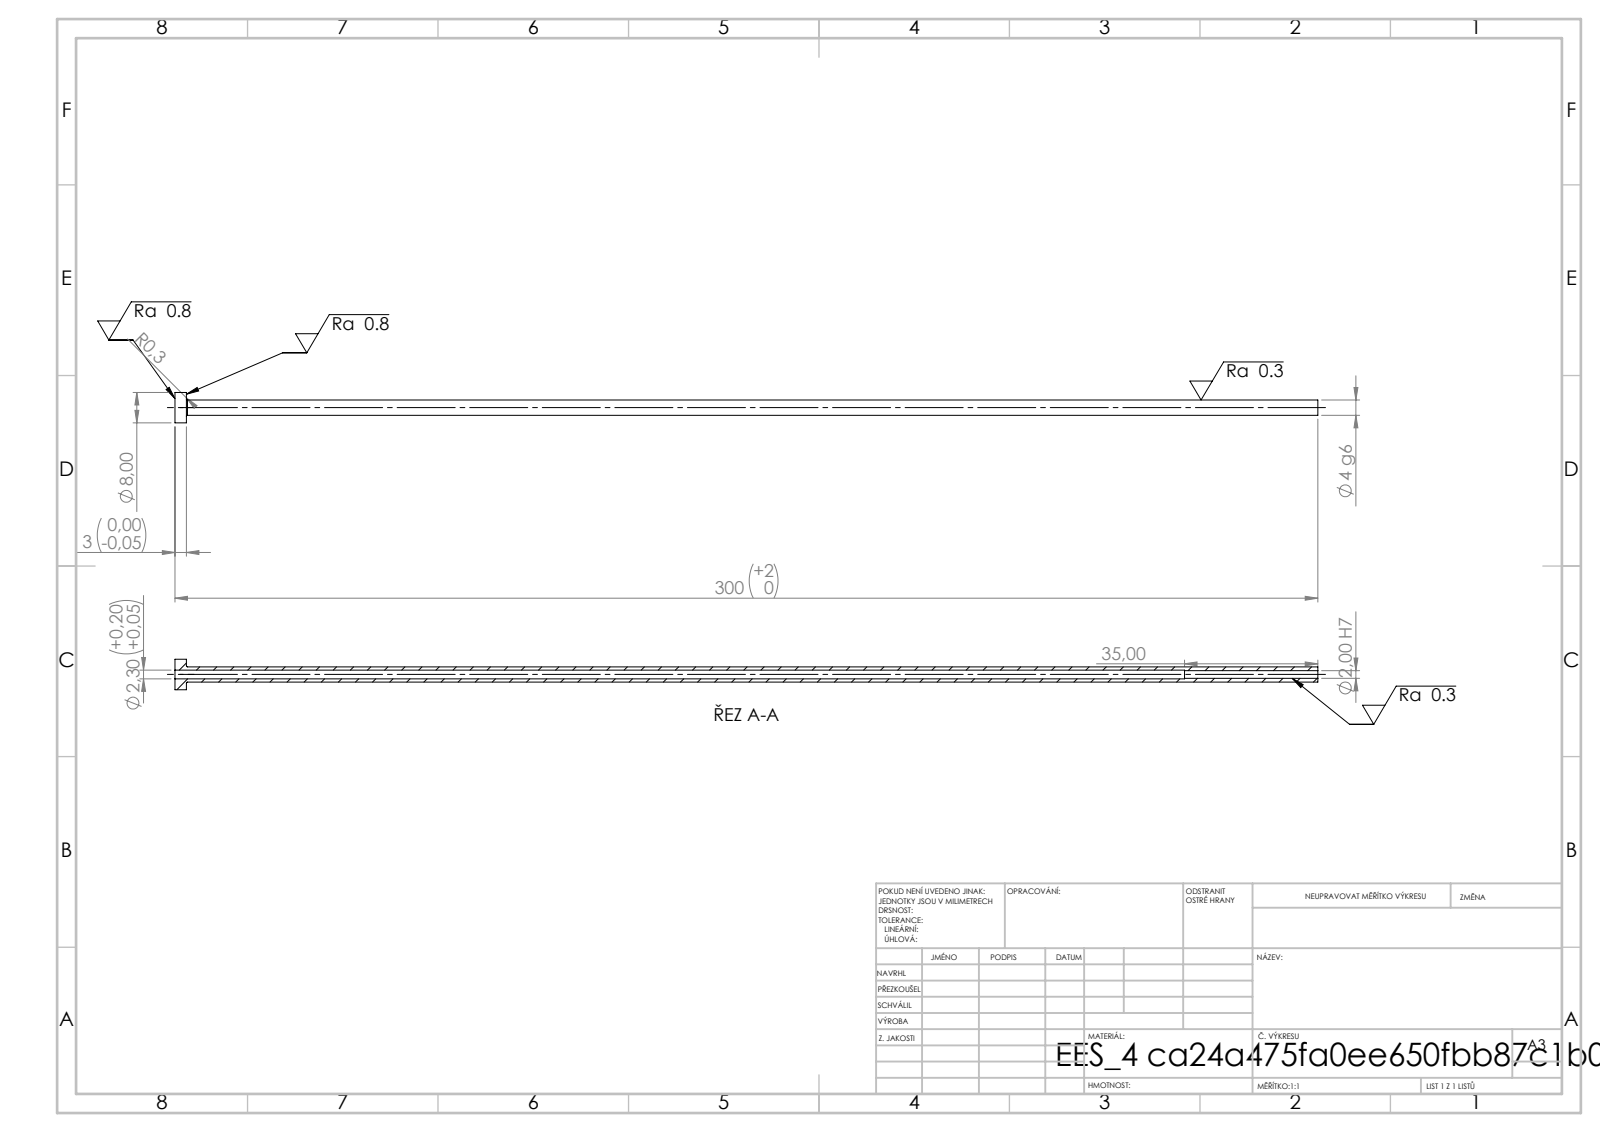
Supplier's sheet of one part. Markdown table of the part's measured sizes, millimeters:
| quantity | value |
| --- | --- |
| STEP written by | SolidWorks 2019 (CONFIG_CONTROL_DESIGN) |
| units | millimeters |
| bodies | 1 solid, 14 faces (4 planar, 8 cylindrical, 2 other) |
| overall size | 300 × 8 × 8 |
| volume | 2 672 mm³ |
| surface area | 6 035 mm² |
| round holes (diameter × count) | 2 × 1, 2.3 × 1 |
| round bosses / shafts (diameter × count) | 8 × 1, 4 × 1 |
| main face-to-face distances | 3, 300, 297, 265, 262, 35 |
